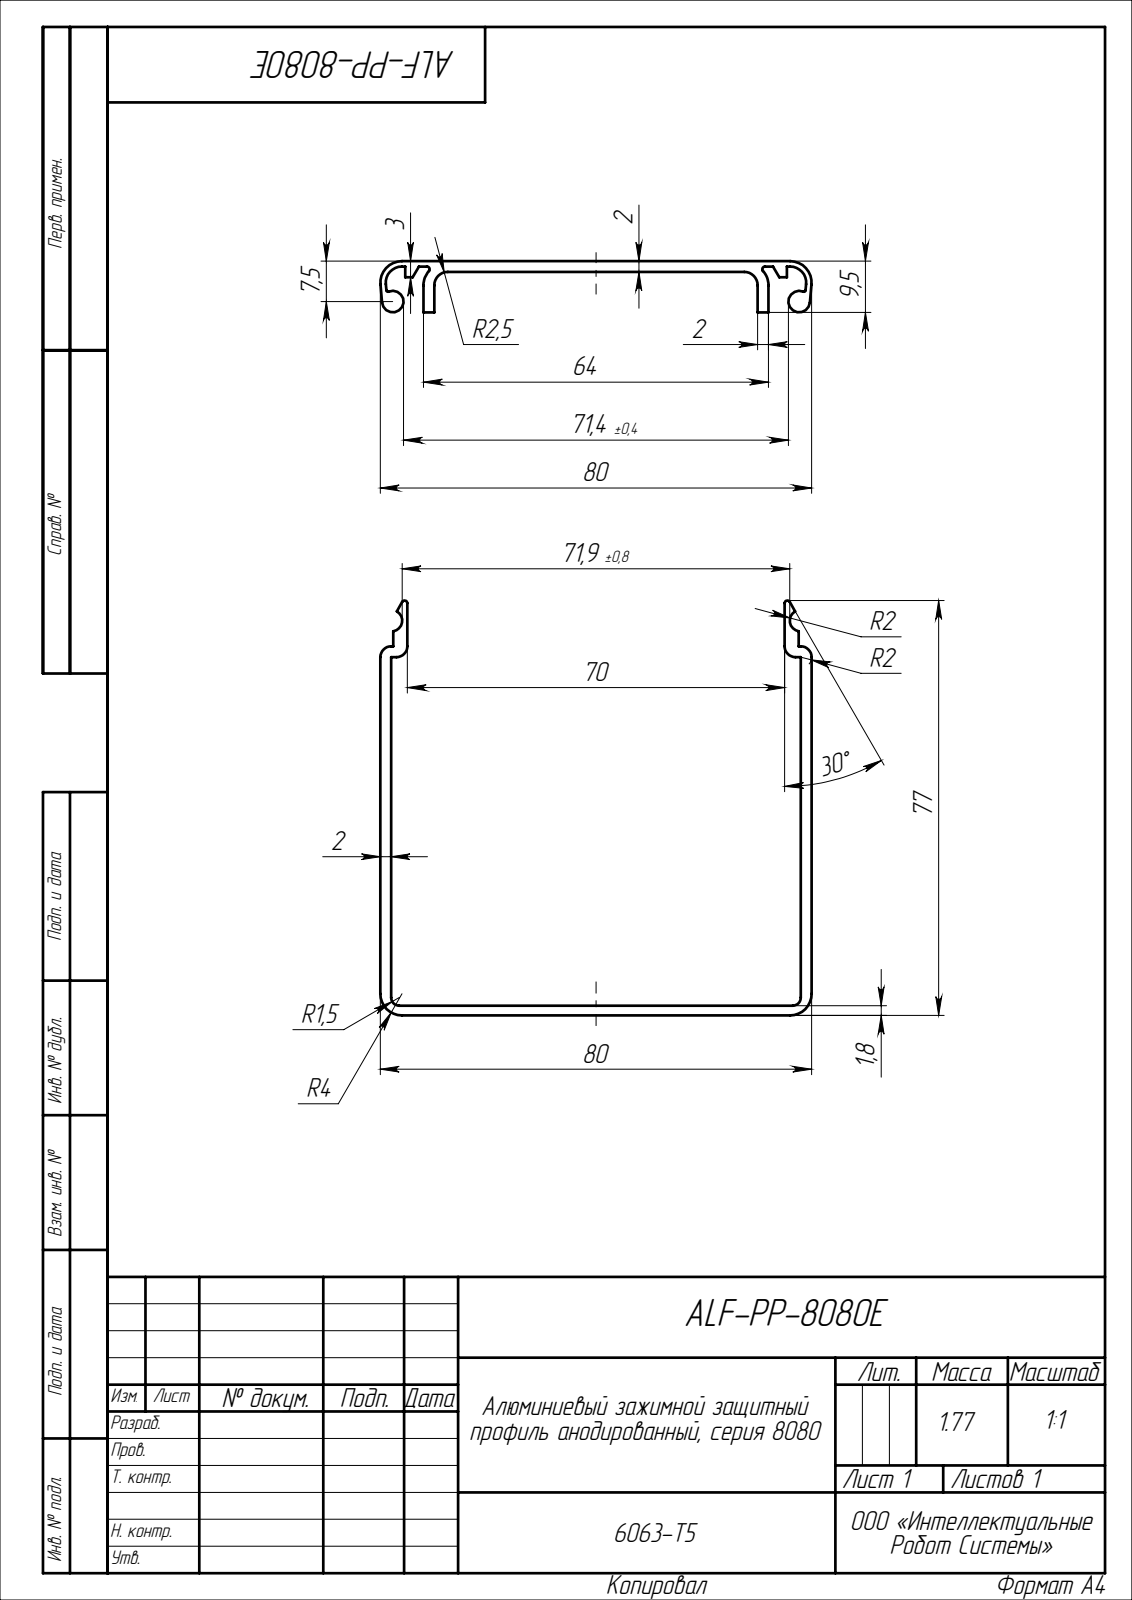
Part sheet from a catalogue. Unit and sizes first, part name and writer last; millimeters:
Units: millimetres
Overall size (bounding box): 1000 × 140 × 80
Round bosses / shafts (diameter × count): ⌀4 ×2
Partial cylindrical surfaces — rounded edges, fillets, slot ends (radius × count): R2 ×6, R4 ×6, R0.5 ×4, R0.3 ×2, R1.5 ×2, R2.5 ×2, R3 ×2
Main face-to-face distances: 2, 78, 1.8, 140, 138.2, 76, 80, 138, 136.2, 3
Volume: 657 140 mm³ · Surface area: 704 384 mm²
Bodies: 2 solids, 73 faces (42 planar, 31 cylindrical, 0 other)
Part name (STEP PRODUCT): ALF-PP-4040E_лоток^ALF-PP-8080E; ALF-PP-8080E; ALF-PP-4040E_крышка^ALF-PP-8080E
STEP written by: SolidWorks 2022 (CONFIG_CONTROL_DESIGN)
